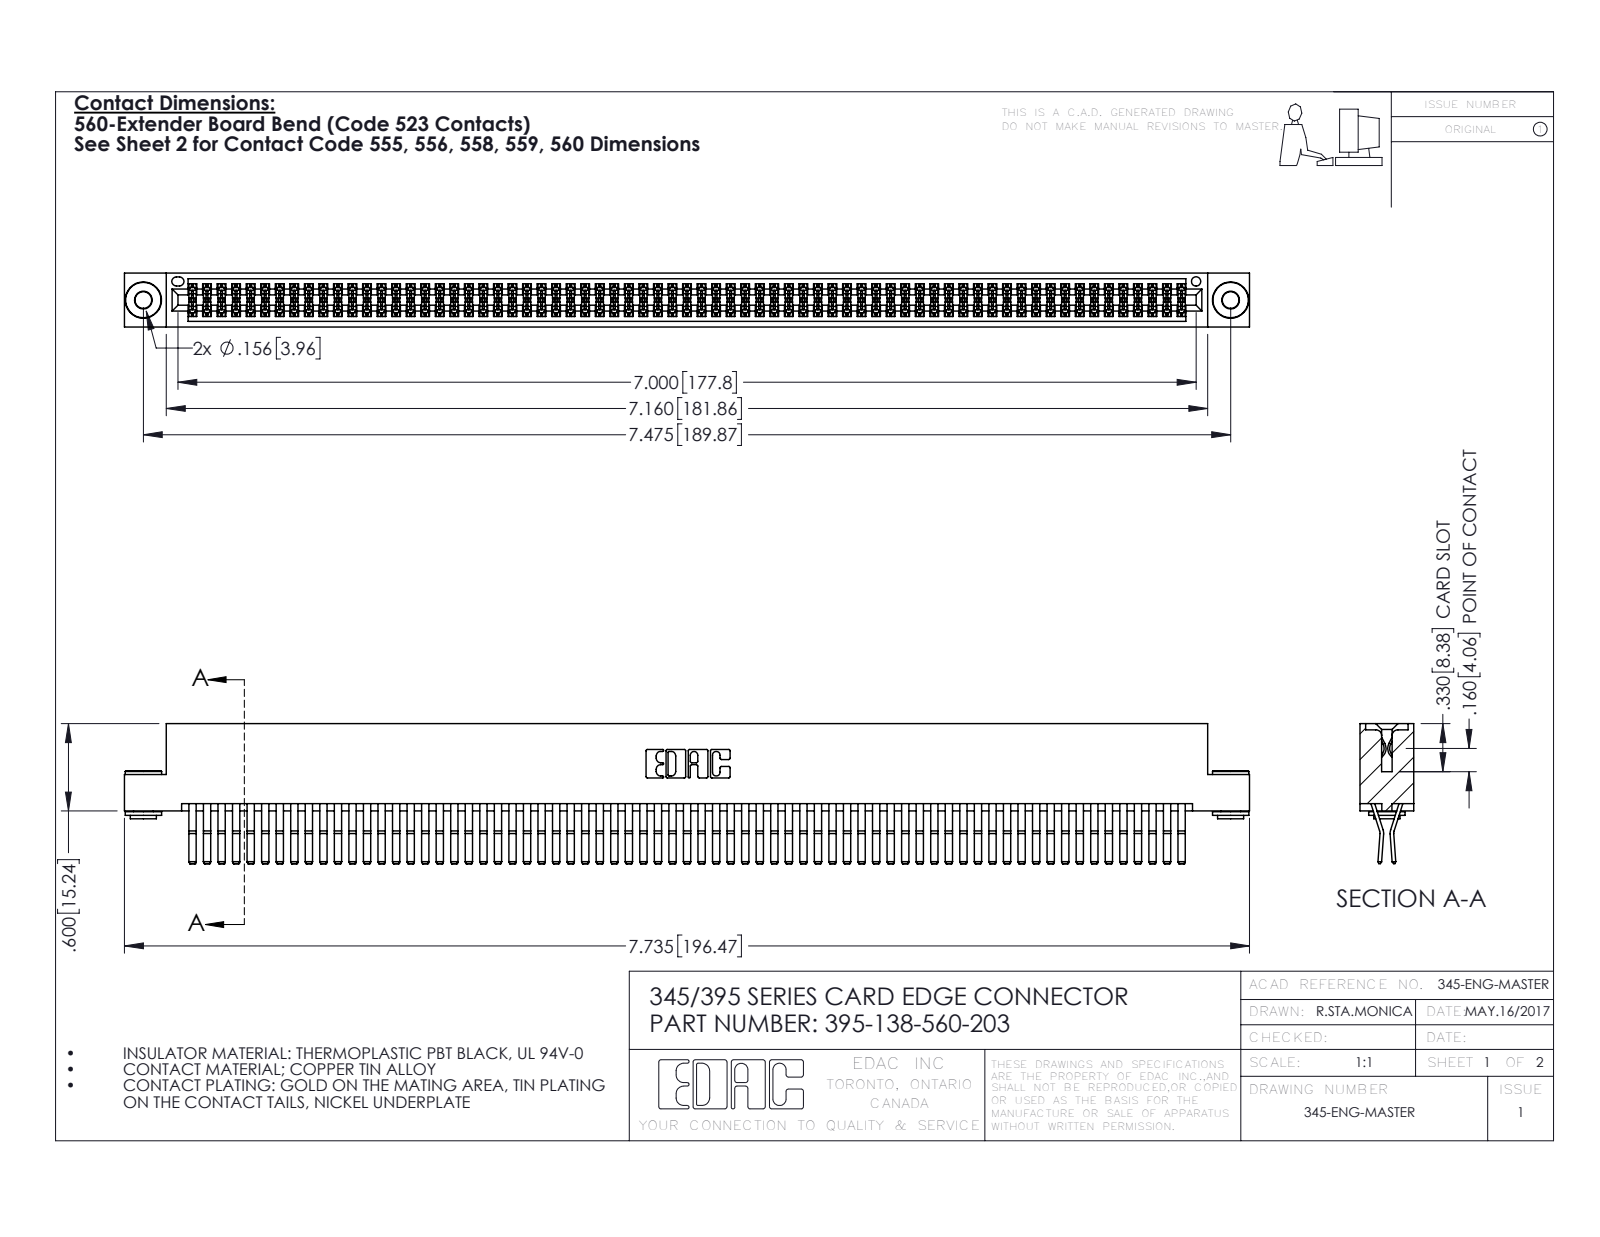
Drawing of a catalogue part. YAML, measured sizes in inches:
part_name: "395-138-560-203; 345-292-001_560 Tail; 345 Part_Flush Mounting Lugs - 0.156 Dia-TH; 345-250-002_345-250-002-102"
step_written_by: "SolidWorks 2016 (CONFIG_CONTROL_DESIGN)"
units: inches
bodies: {solids: 141, faces: 7340, planar: 4644, cylindrical: 2688, other: 8}
overall_size: [7.735, 0.962, 0.37]
volume: 1.236
surface_area: 51.15
round_holes:
  - {diameter: 0.116, count: 2}
  - {diameter: 0.156, count: 2}
  - {diameter: 0.064, count: 1}
round_bosses_or_shafts:
  - {diameter: 0.25, count: 2}
  - {diameter: 0.18, count: 2}
  - {diameter: 0.136, count: 2}
partial_cylinders:
  - {radius: 0.006, count: 207}
  - {radius: 0.01, count: 22}
  - {radius: 0.007, count: 6}
  - {radius: 0.031, count: 6}
  - {radius: 0.026, count: 3}
  - {radius: 0.01, count: 2}
  - {radius: 0.014, count: 2}
  - {radius: 0.019, count: 2}
face_to_face_distances: [0.025, 0.072, 0.298, 0.2, 0.37, 0.098, 0.272, 0.225, 0.175, 0.149]
hole_center_spacings: [0.27, 7.239, 7.475]
